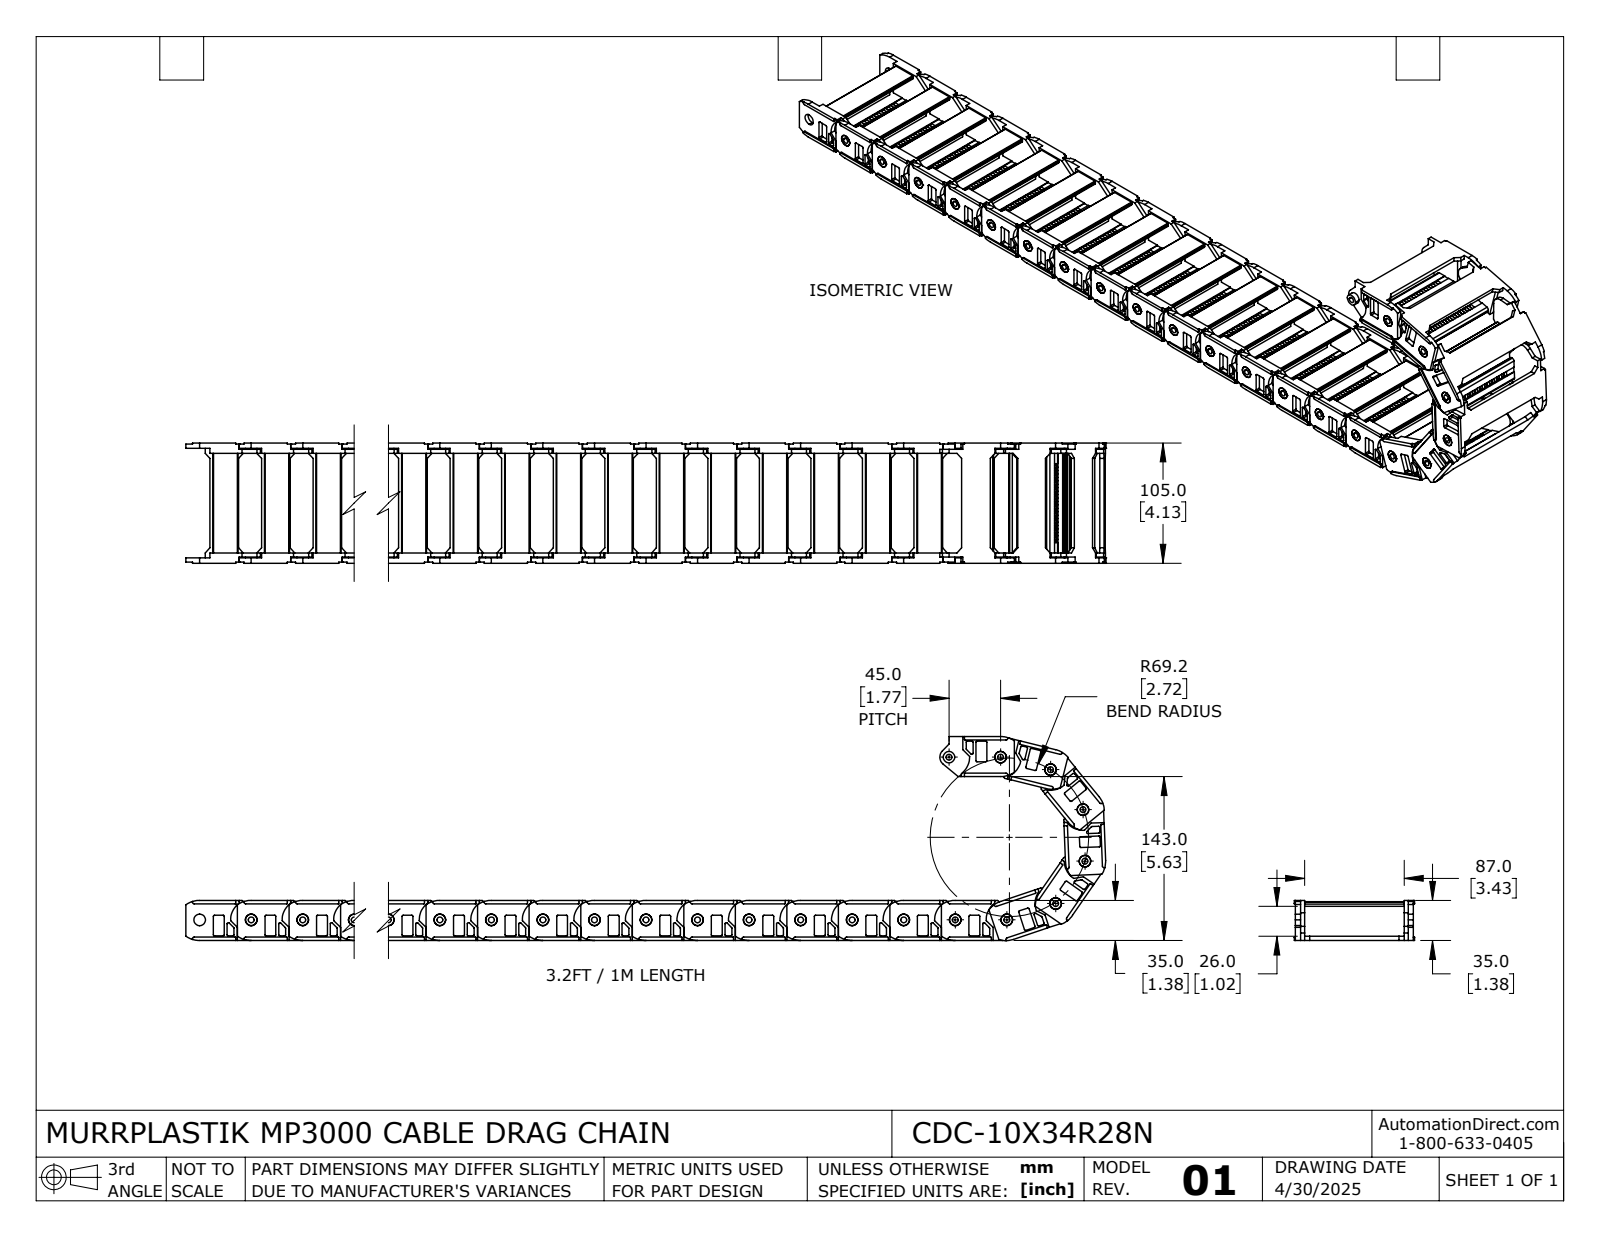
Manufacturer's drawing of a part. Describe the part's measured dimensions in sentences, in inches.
The part is named "CDC-10X34R28N". Its 3-D file was written by "SolidWorks 2024 (AUTOMOTIVE_DESIGN)". It is 22 solids with 5104 faces: 4004 planar, 1100 cylindrical and 0 other. Overall it measures 32.216 by 7.013 by 4.134 inches. Its volume is 47.13 cubic inches and its surface area 739 square inches. Round holes: 22 of diameter 0.201, 22 of diameter 0.398. Round bosses or shafts: 22 of diameter 0.394. Partial cylindrical surfaces (rounded edges, fillets, slot ends): 176 of radius 0.039, 88 of radius 0.02, 44 of radius 0.059, 44 of radius 0.079, 44 of radius 0.827, 22 of radius 0.11, 22 of radius 0.315, 22 of radius 0.709. The main face-to-face distances are 3.74, 0.157, 0.315, 0.15, 1.181, 1.331, 0.146, 3.909, 0.169, 3.594. The hole center spacings are 1.772, 3.543, 5.315, 7.087, 8.858, 10.63, 12.402, 14.173.
